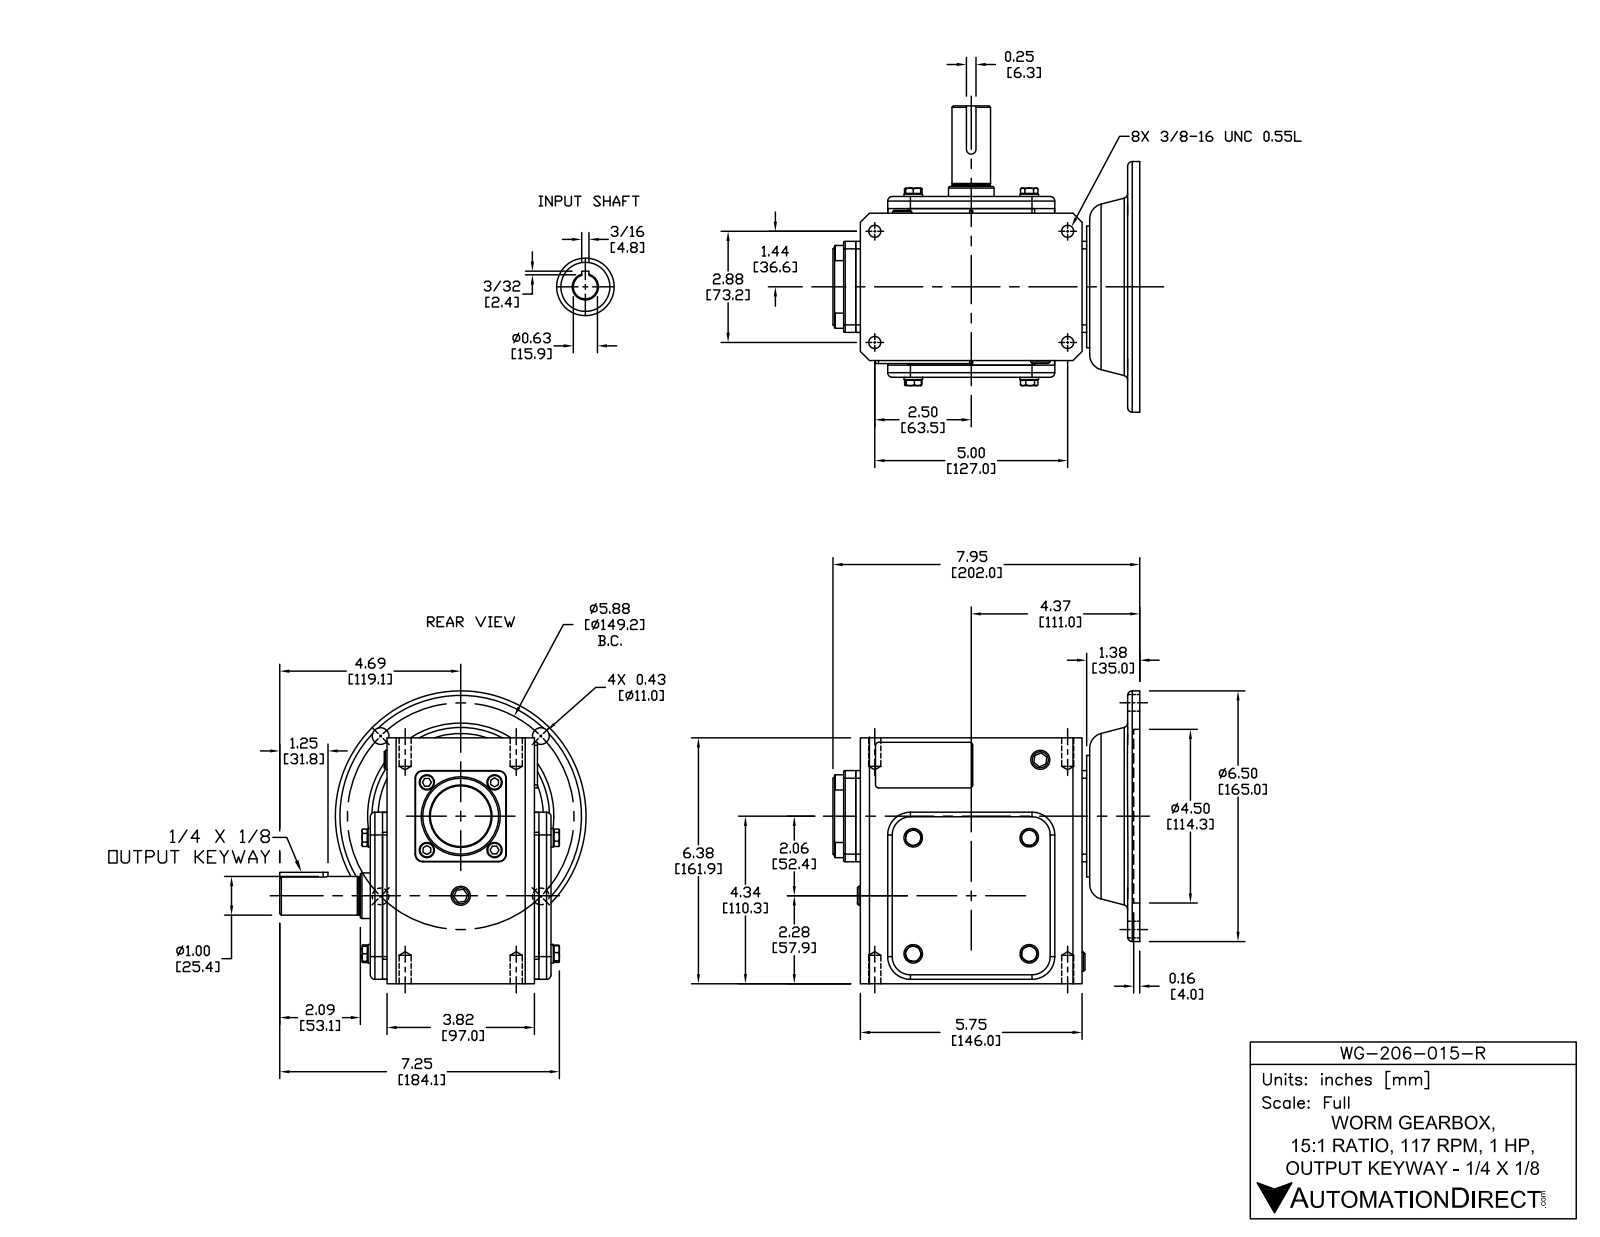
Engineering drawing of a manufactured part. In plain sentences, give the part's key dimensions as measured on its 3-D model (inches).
The part is named "WG-206-015-R". Its 3-D file was written by "SolidWorks 2015 (CONFIG_CONTROL_DESIGN)". It is 43 solids with 610 faces: 300 planar, 182 cylindrical and 128 other. Overall it measures 7.953 by 7.938 by 7.591 inches. Its volume is 171.8 cubic inches and its surface area 407.7 square inches. Round holes: 4 of diameter 0.313, 4 of diameter 0.406, 1 of diameter 0.591, 1 of diameter 0.625, 1 of diameter 1.181, 1 of diameter 1.457, 1 of diameter 1.654, 1 of diameter 3.543, 1 of diameter 4.5. Round bosses or shafts: 8 of diameter 0.394, 4 of diameter 0.48, 1 of diameter 6.496, 1 of diameter 3.15, 1 of diameter 2.047, 1 of diameter 1.575, 1 of diameter 1.181, 1 of diameter 1.142. Partial cylindrical surfaces (rounded edges, fillets, slot ends): 8 of radius 0.079, 8 of radius 0.118, 4 of radius 0.197, 4 of radius 0.591, 2 of radius 0.02, 2 of radius 0.039, 1 of radius 0.125, 1 of radius 2.717. The main face-to-face distances are 0.315, 0.118, 4.055, 4.37, 0.433, 4.252, 3.937, 6.375, 4.685, 0.709. The hole center spacings are 2.937, 4.154, 2.077, 2.88, 4.631, 5, 5.77, 5.875.
